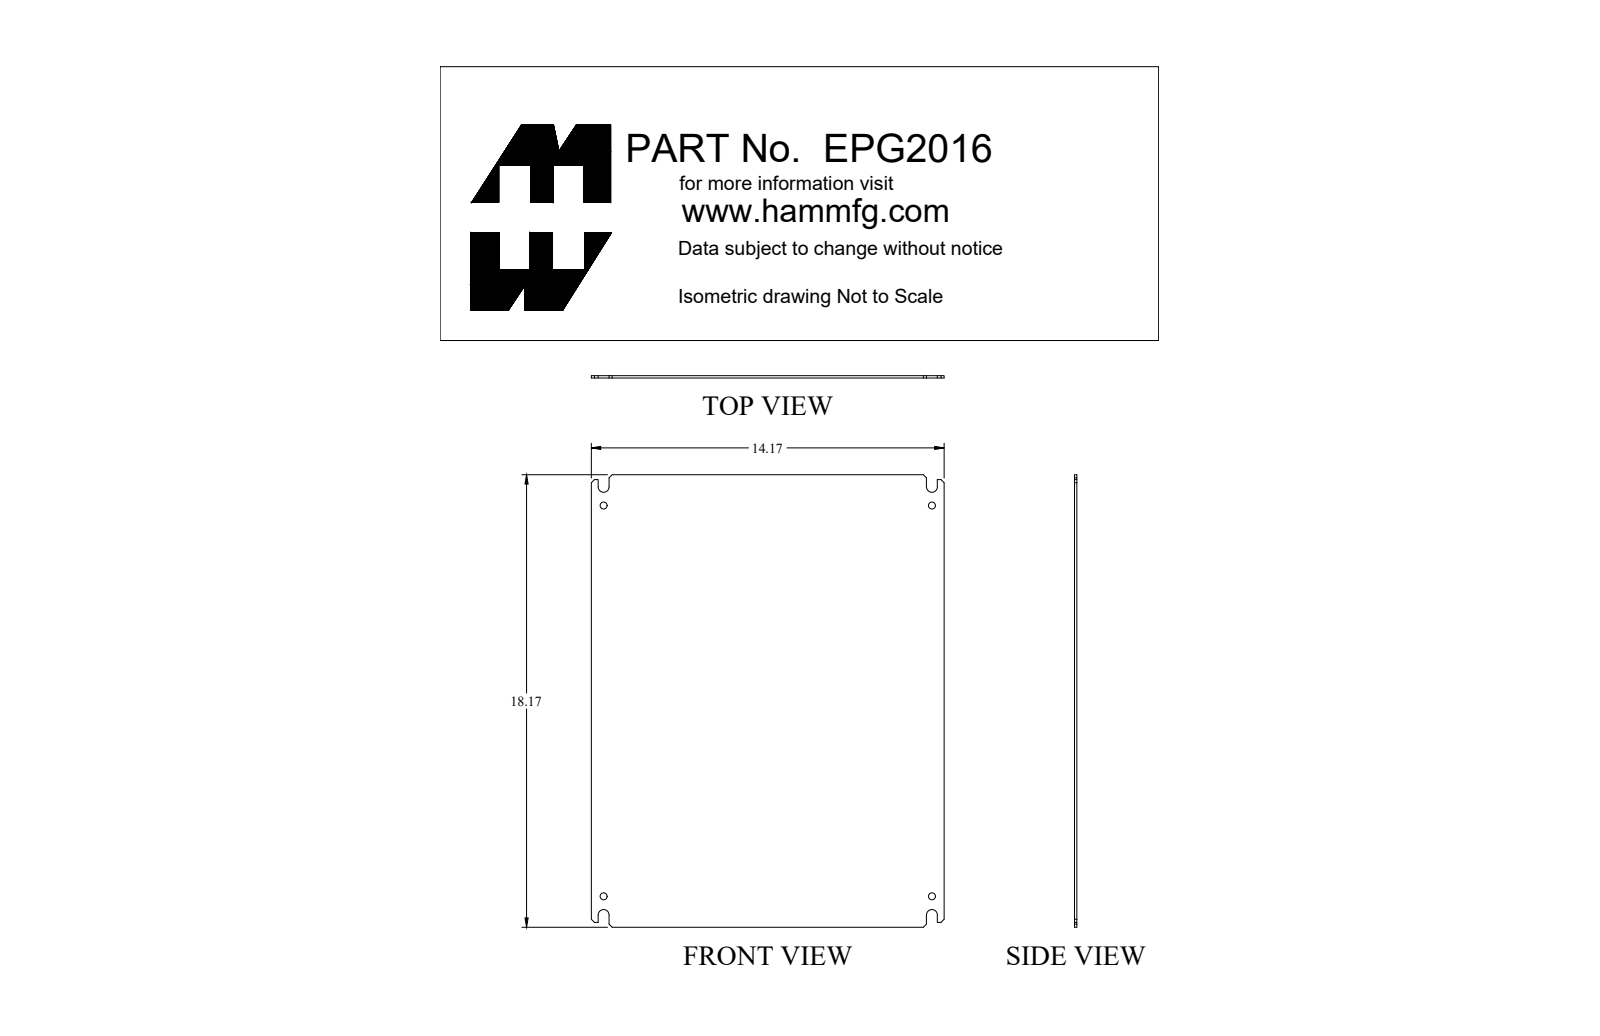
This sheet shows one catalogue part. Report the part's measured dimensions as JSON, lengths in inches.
{"part_name": "EPG2016", "step_written_by": "SolidWorks 2018 (AUTOMOTIVE_DESIGN)", "units": "inches", "bodies": {"solids": 1, "faces": 40, "planar": 26, "cylindrical": 14, "other": 0}, "overall_size": [18.17, 14.17, 0.095], "volume_in3": 24.3, "surface_area_in2": 518.3, "round_holes": [[0.281, 4]], "partial_cylinders_radius": [[0.219, 4]], "face_to_face_distances": [0.095, 14.17, 18.17, 0.709, 13.461, 0.272, 13.898, 0.437, 13.188, 12.751], "hole_center_spacings": [13.188, 15.688, 20.495]}
